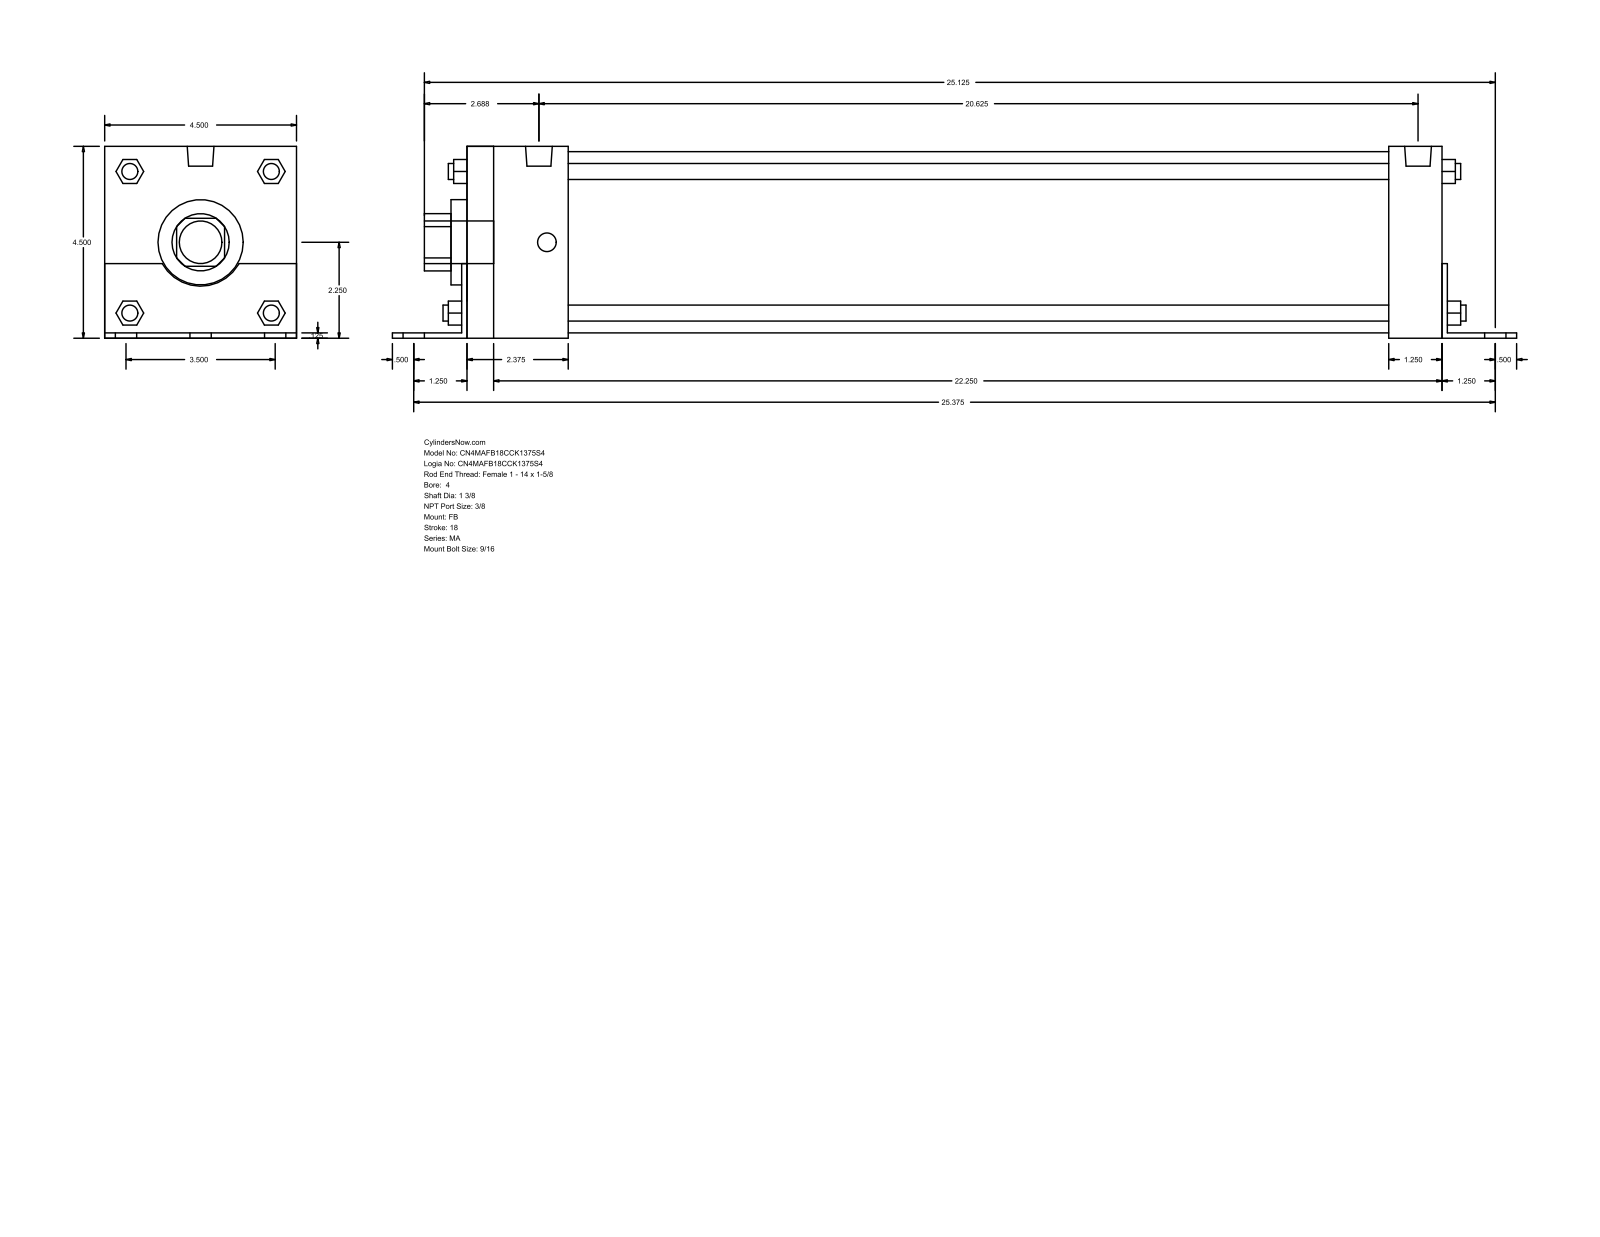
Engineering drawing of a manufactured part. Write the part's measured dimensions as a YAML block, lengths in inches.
part_name: "MA_FB__0400_1.375"
step_written_by: "GSSL Pune (CONFIG_CONTROL_DESIGN)"
units: inches
bodies: {solids: 0, faces: 140, planar: 105, cylindrical: 35, other: 0}
overall_size: [26.375, 4.502, 4.5]
round_holes:
  - {diameter: 1.375, count: 1}
  - {diameter: 2, count: 1}
  - {diameter: 4.25, count: 1}
round_bosses_or_shafts:
  - {diameter: 0.563, count: 6}
  - {diameter: 0.437, count: 4}
  - {diameter: 0.375, count: 4}
  - {diameter: 0.627, count: 2}
  - {diameter: 1, count: 1}
partial_cylinders:
  - {radius: 0.672, count: 1}
  - {radius: 1.03, count: 1}
face_to_face_distances: [4.5, 0.125, 4.502, 0.123, 4.377, 22.875, 0.125, 23, 1.375, 2.375]
